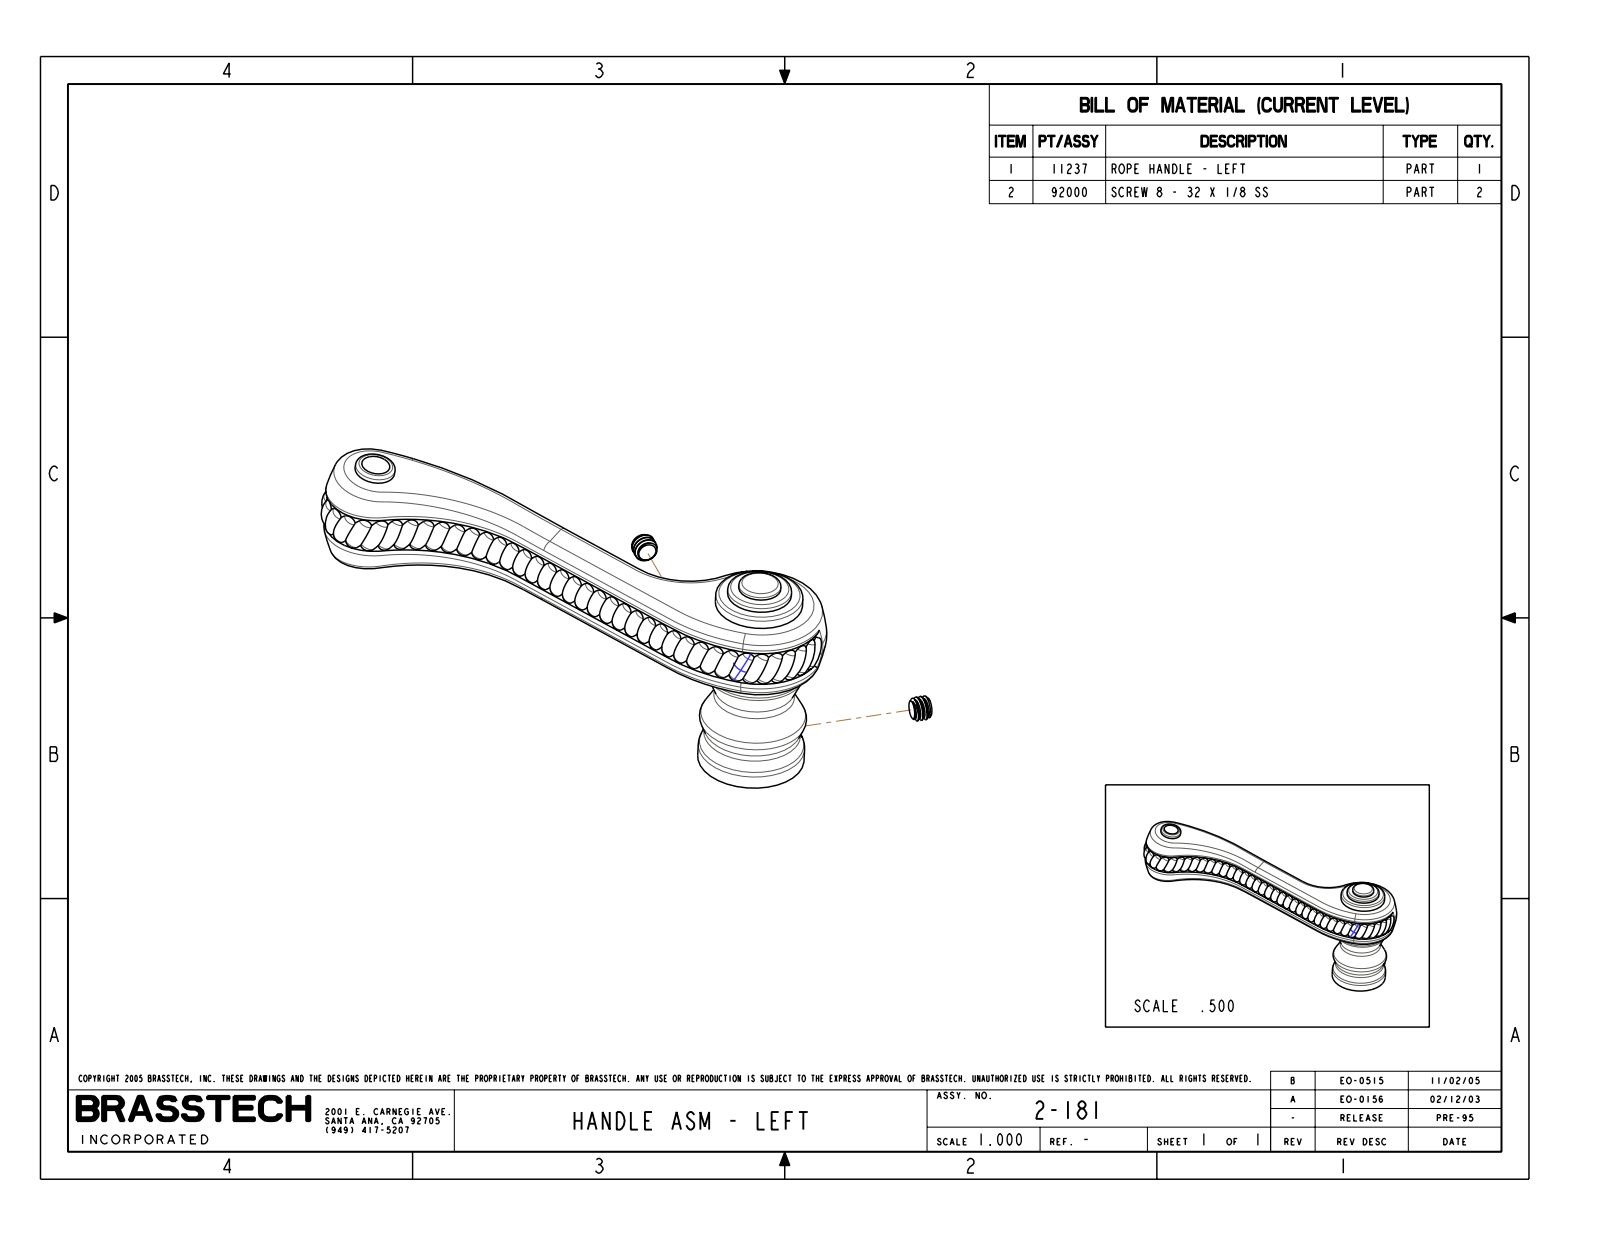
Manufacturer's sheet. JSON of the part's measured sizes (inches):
{"part_name": "11237; 92000; 2-181_ASM", "step_written_by": "CREO PARAMETRIC BY PTC INC, 2018400 (CONFIG_CONTROL_DESIGN)", "units": "inches", "bodies": {"solids": 3, "faces": 583, "planar": 111, "cylindrical": 94, "other": 378}, "overall_size": [3.825, 1.46, 0.977], "volume_in3": 1.215, "surface_area_in2": 21.92, "round_holes": [[0.13, 2], [0.339, 1], [0.45, 1]], "round_bosses_or_shafts": [[0.26, 2], [0.164, 2], [0.73, 1], [0.7, 1], [0.6, 1], [0.44, 1], [0.29, 1]], "partial_cylinders_radius": [[11, 2], [0.187, 1]], "face_to_face_distances": [0.49, 0.8, 1.29, 0.08, 0.147, 0.57, 1.37, 0.05, 1.42, 0.62]}
